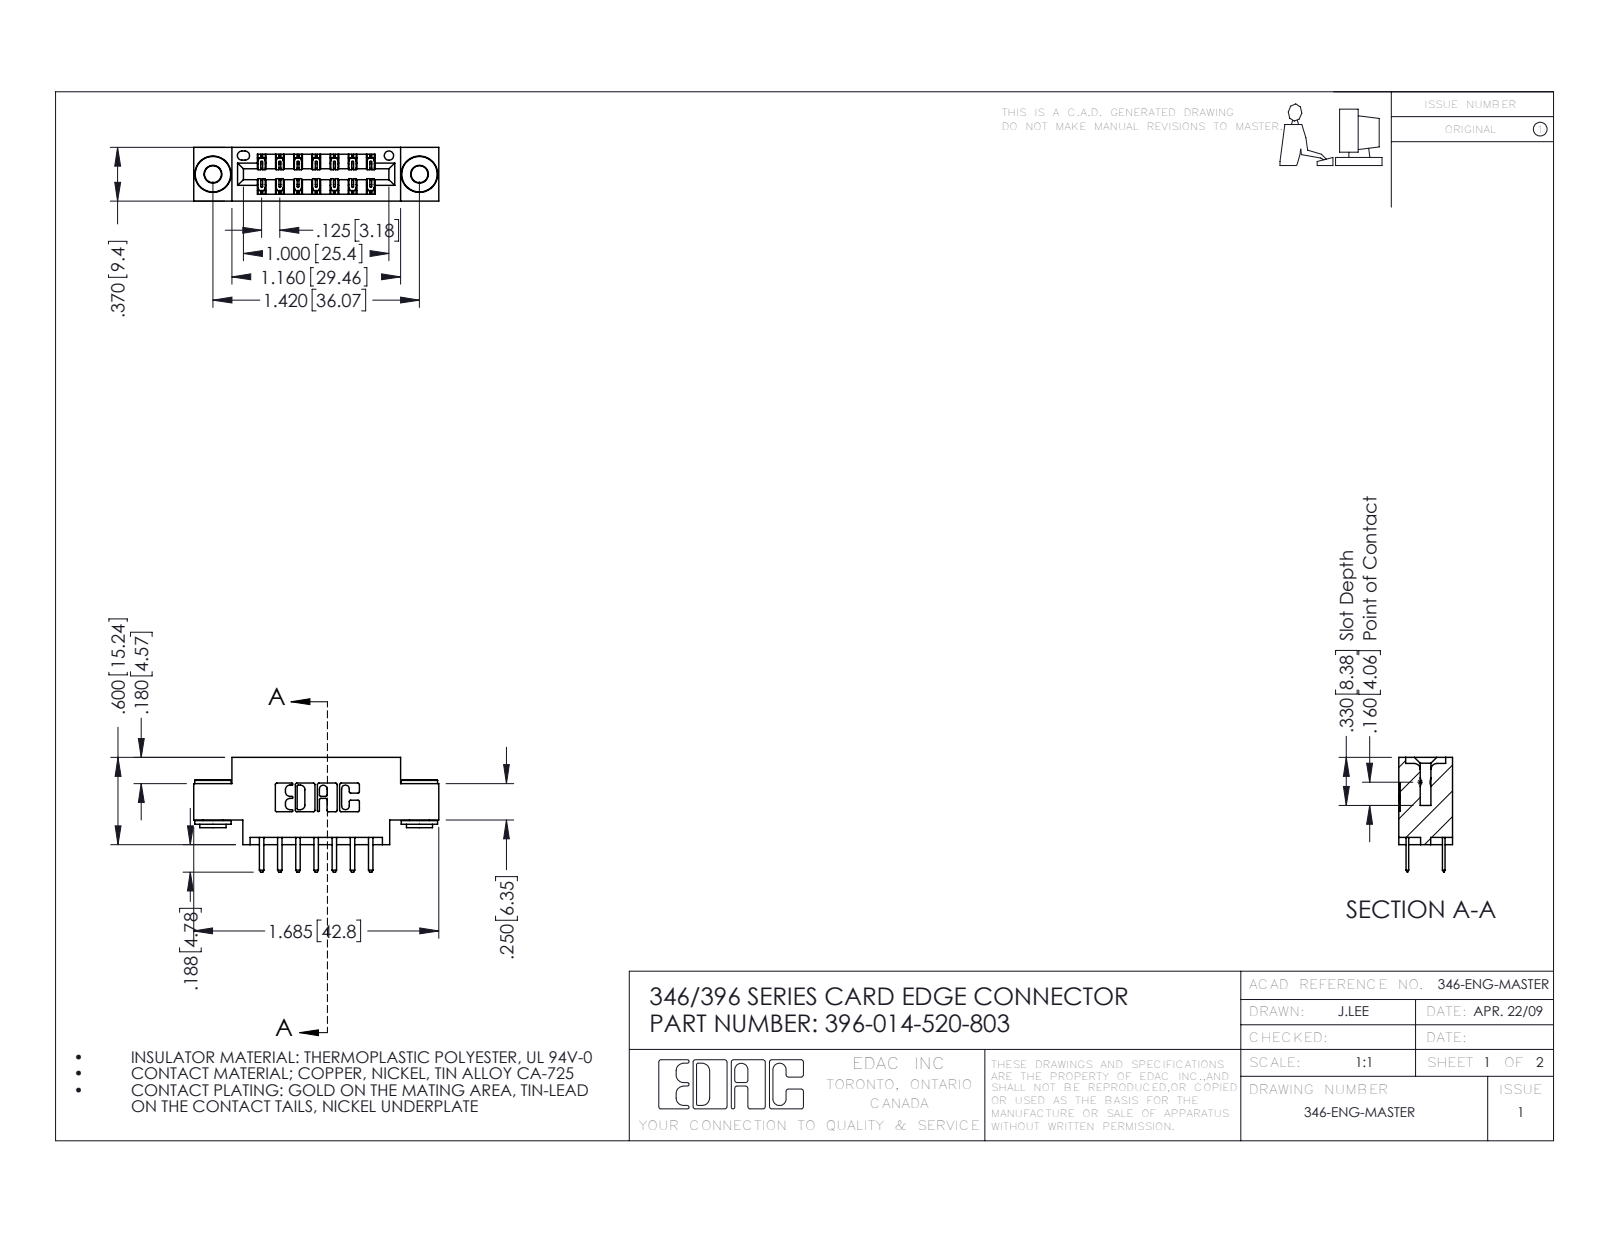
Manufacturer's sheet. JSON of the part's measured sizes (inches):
{"part_name": "345-292-001_345-293-120; 345-250-002_345-250-002-102; 396-014-520-803; 346 Part_0.170 Offset - 0.156 Dia-TH", "step_written_by": "SolidWorks 2016 (CONFIG_CONTROL_DESIGN)", "units": "inches", "bodies": {"solids": 17, "faces": 948, "planar": 608, "cylindrical": 332, "other": 8}, "overall_size": [1.685, 0.788, 0.37], "volume_in3": 0.229, "surface_area_in2": 7.747, "round_holes": [[0.116, 2], [0.156, 2], [0.064, 1]], "round_bosses_or_shafts": [[0.25, 2], [0.18, 2], [0.136, 2]], "partial_cylinders_radius": [[0.01, 22], [0.006, 21], [0.01, 18], [0.007, 6], [0.031, 6], [0.026, 3], [0.014, 2], [0.022, 2]], "face_to_face_distances": [0.25, 0.37, 0.048, 0.322, 0.025, 0.275, 0.148, 0.222, 0.1, 0.174], "hole_center_spacings": [0.246, 1.217, 1.42]}
